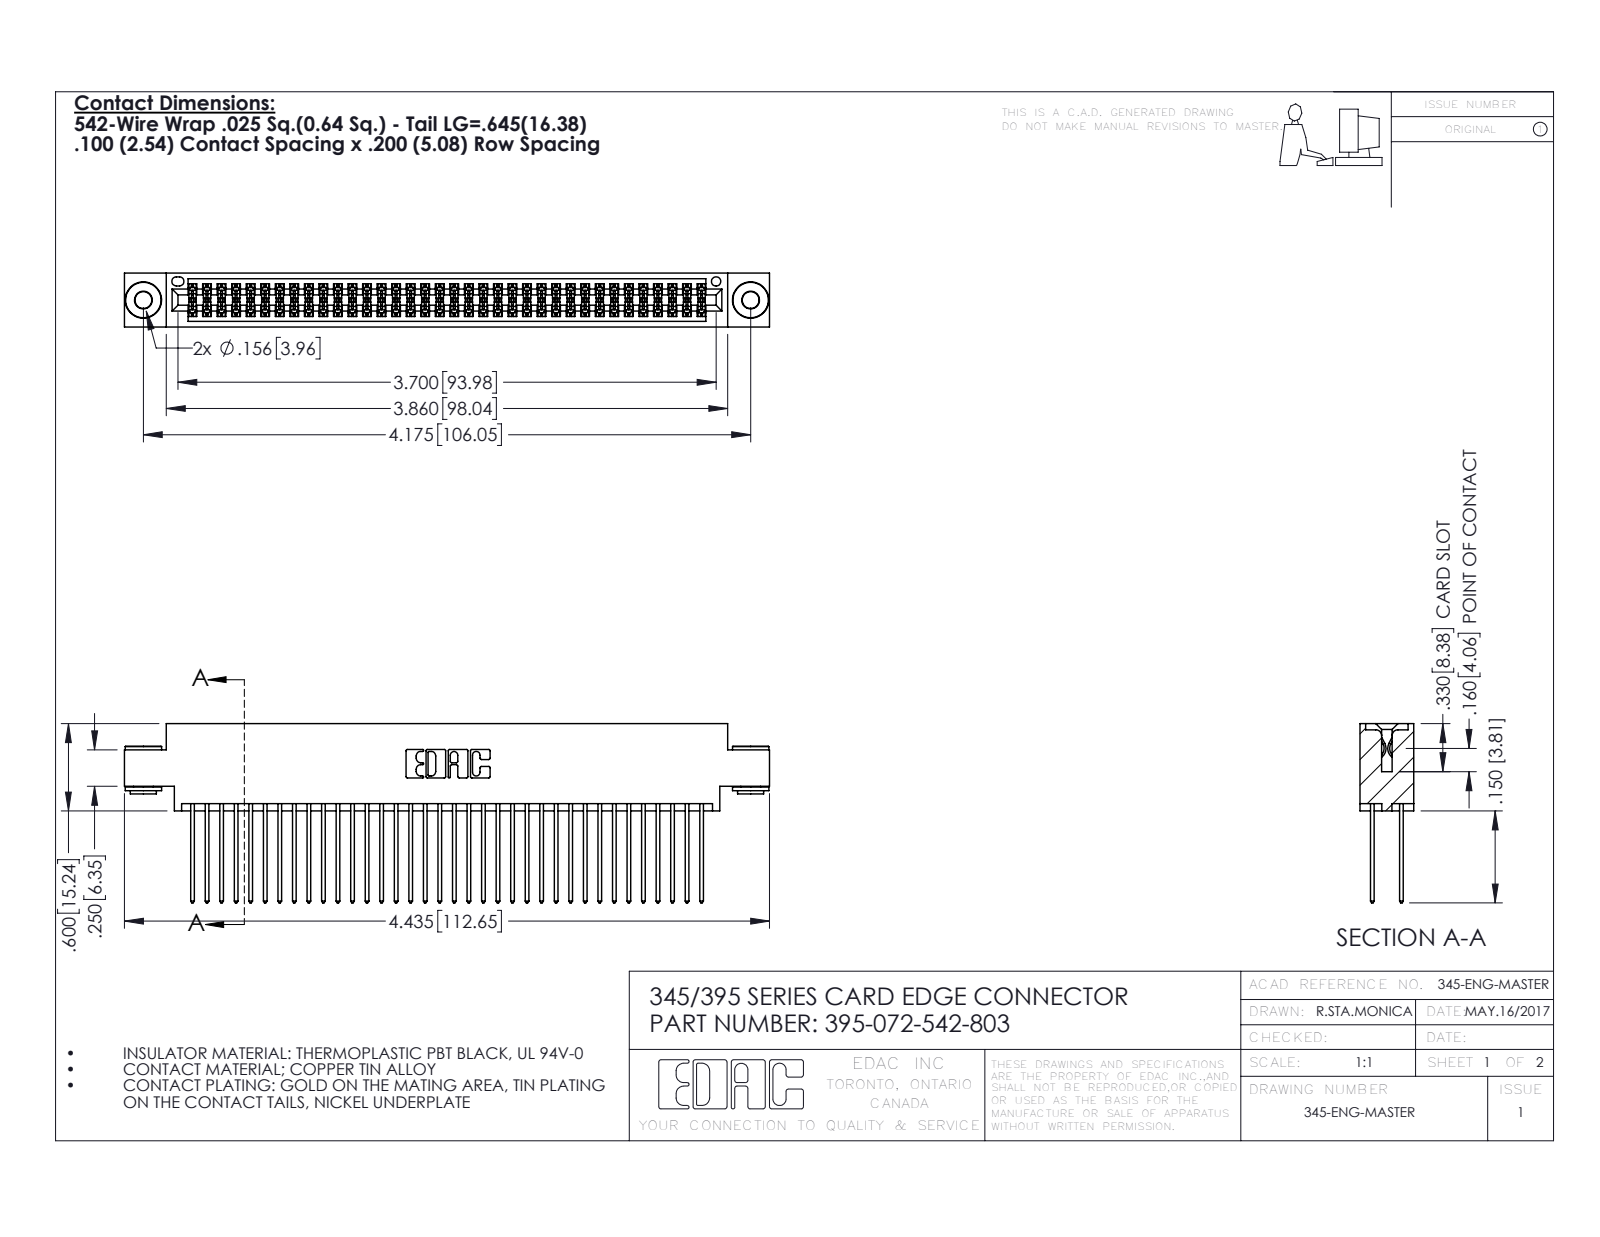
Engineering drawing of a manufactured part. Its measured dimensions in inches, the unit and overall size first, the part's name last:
Units: inches
Overall size (bounding box): 4.435 × 1.232 × 0.37
Round holes (diameter × count): ⌀0.116 ×2, ⌀0.156 ×2, ⌀0.064 ×1
Round bosses / shafts (diameter × count): ⌀0.25 ×2, ⌀0.18 ×2, ⌀0.136 ×2
Partial cylindrical surfaces — rounded edges, fillets, slot ends (radius × count): R0.006 ×108, R0.01 ×72, R0.01 ×22, R0.007 ×6, R0.031 ×6, R0.026 ×3, R0.014 ×2, R0.019 ×2
Main face-to-face distances: 0.072, 0.298, 0.2, 0.098, 0.272, 0.025, 0.37, 0.225, 0.175, 0.149
Hole centre spacings: 0.27, 3.939, 4.175
Volume: 0.679 in³ · Surface area: 28.29 in²
Bodies: 75 solids, 3768 faces (2470 planar, 1290 cylindrical, 8 other)
Part name (STEP PRODUCT): 345-250-002_345-250-002-102; 395-072-542-803; 345 Part_0.170 Offset - 0.156 Dia-TH; 345-292-001_345-293-142
STEP written by: SolidWorks 2016 (CONFIG_CONTROL_DESIGN)
